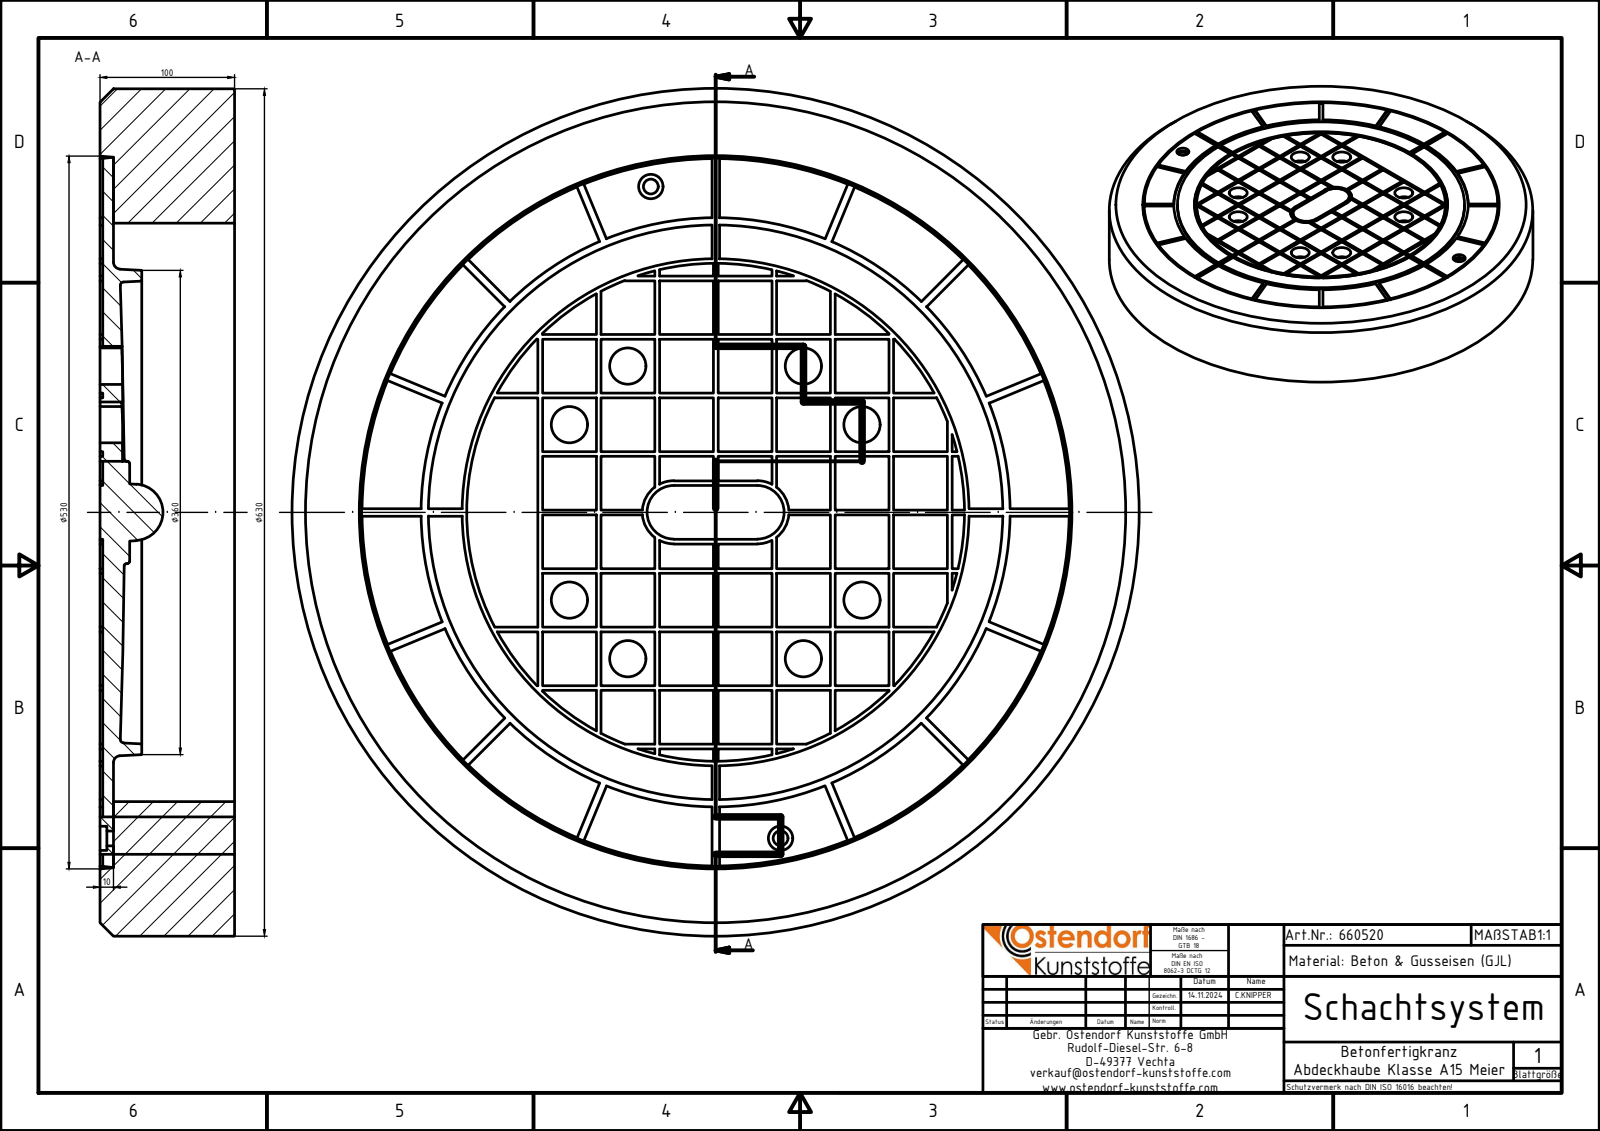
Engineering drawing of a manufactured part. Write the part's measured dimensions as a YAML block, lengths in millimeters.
part_name: "660520z; 660520z Betonkranz; 660520z Schachtabdeckung"
step_written_by: "Autodesk Inventor 2024 (AUTOMOTIVE_DESIGN)"
units: millimeters
bodies: {solids: 2, faces: 482, planar: 393, cylindrical: 78, other: 11}
overall_size: [630, 630, 100]
volume: 18740000
surface_area: 1182000
round_holes:
  - {diameter: 27, count: 8}
  - {diameter: 11, count: 2}
  - {diameter: 18, count: 2}
  - {diameter: 377, count: 1}
  - {diameter: 430, count: 1}
  - {diameter: 438, count: 1}
round_bosses_or_shafts:
  - {diameter: 630, count: 1}
  - {diameter: 427, count: 1}
  - {diameter: 370, count: 1}
partial_cylinders:
  - {radius: 20, count: 2}
  - {radius: 23.5, count: 2}
  - {radius: 21, count: 1}
  - {radius: 36.58, count: 1}
face_to_face_distances: [10, 90, 100, 98, 8, 2, 43.5, 87, 130.5, 69]
hole_center_spacings: [126.82, 179.36, 61.52, 130.5, 217.5, 246.07, 253.65, 236.56]
